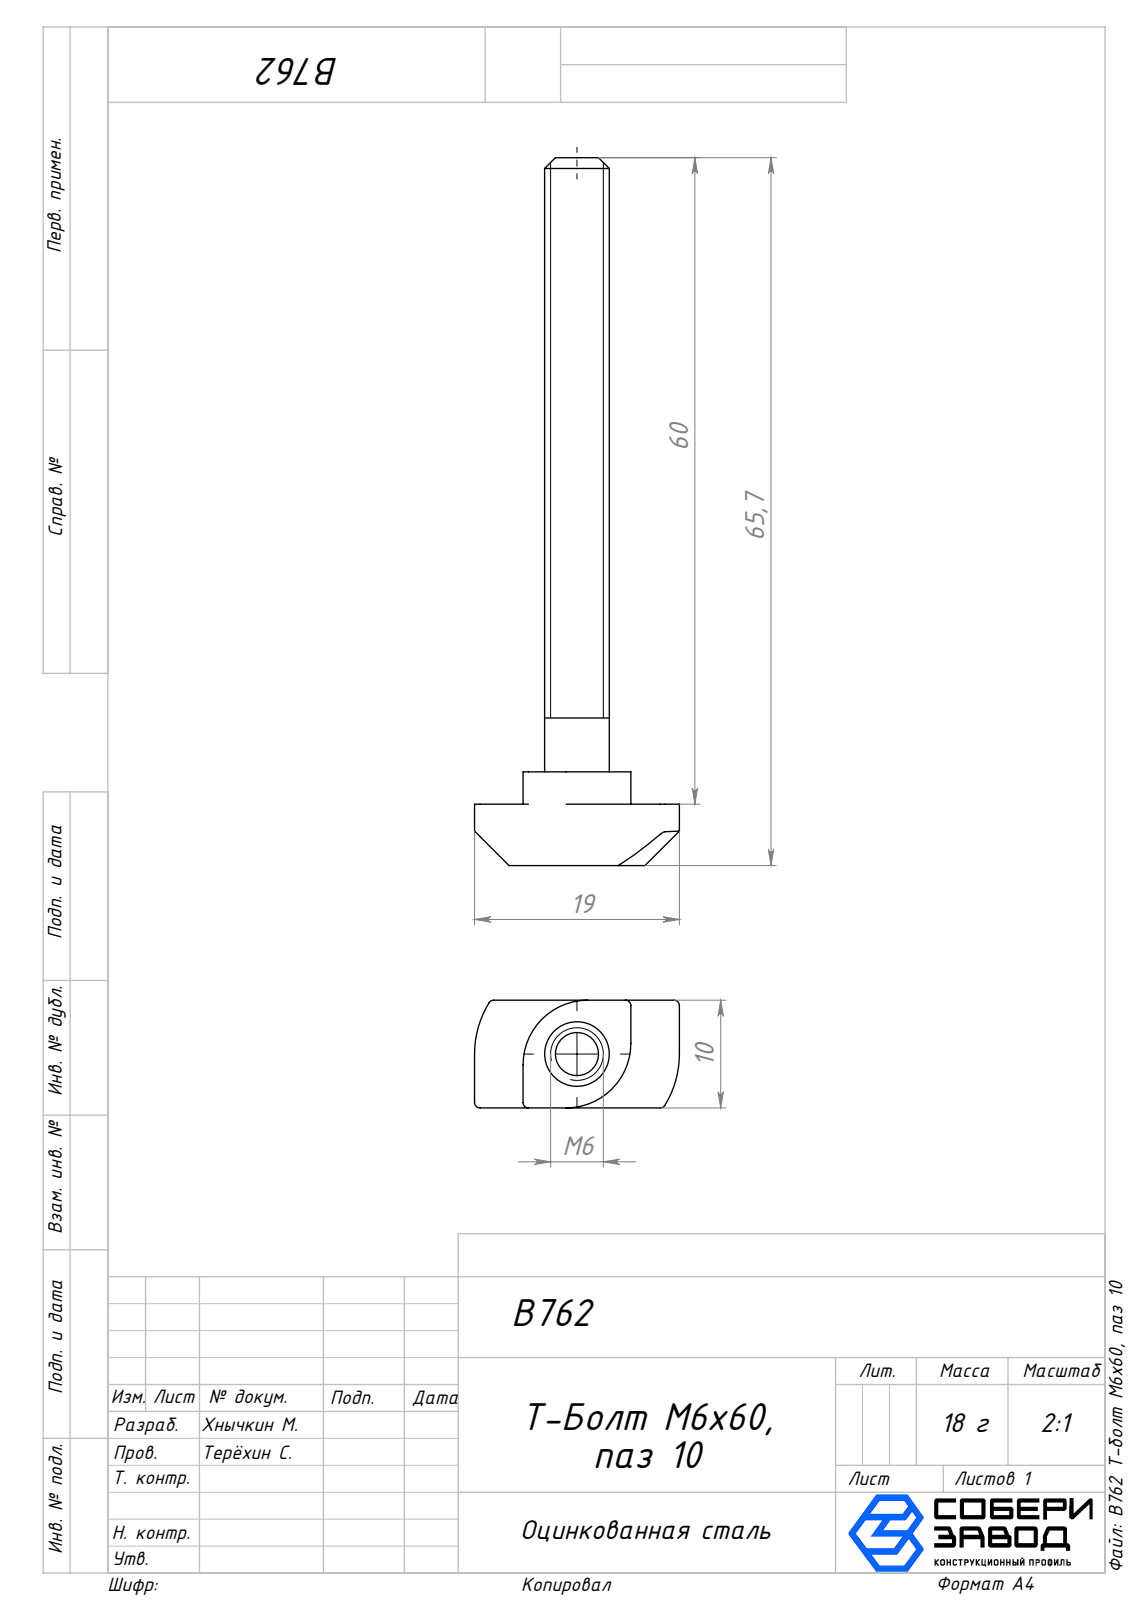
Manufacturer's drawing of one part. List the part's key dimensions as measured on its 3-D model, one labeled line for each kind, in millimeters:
Part name (STEP PRODUCT): B762 Т-болт М6х60, паз 10
STEP written by: SolidWorks 2025 (AUTOMOTIVE_DESIGN)
Units: millimetres
Bodies: 1 solid, 29 faces (13 planar, 12 cylindrical, 4 other)
Overall size (bounding box): 65.7 × 19 × 10
Volume: 2 806 mm³ · Surface area: 1 790 mm²
Round bosses / shafts (diameter × count): ⌀6 ×1
Partial cylindrical surfaces — rounded edges, fillets, slot ends (radius × count): R0.5 ×6, R6 ×2, R9.08 ×2
Main face-to-face distances: 10, 5.7, 8.7, 3, 4.5, 14.5, 65.7, 60, 57, 19
